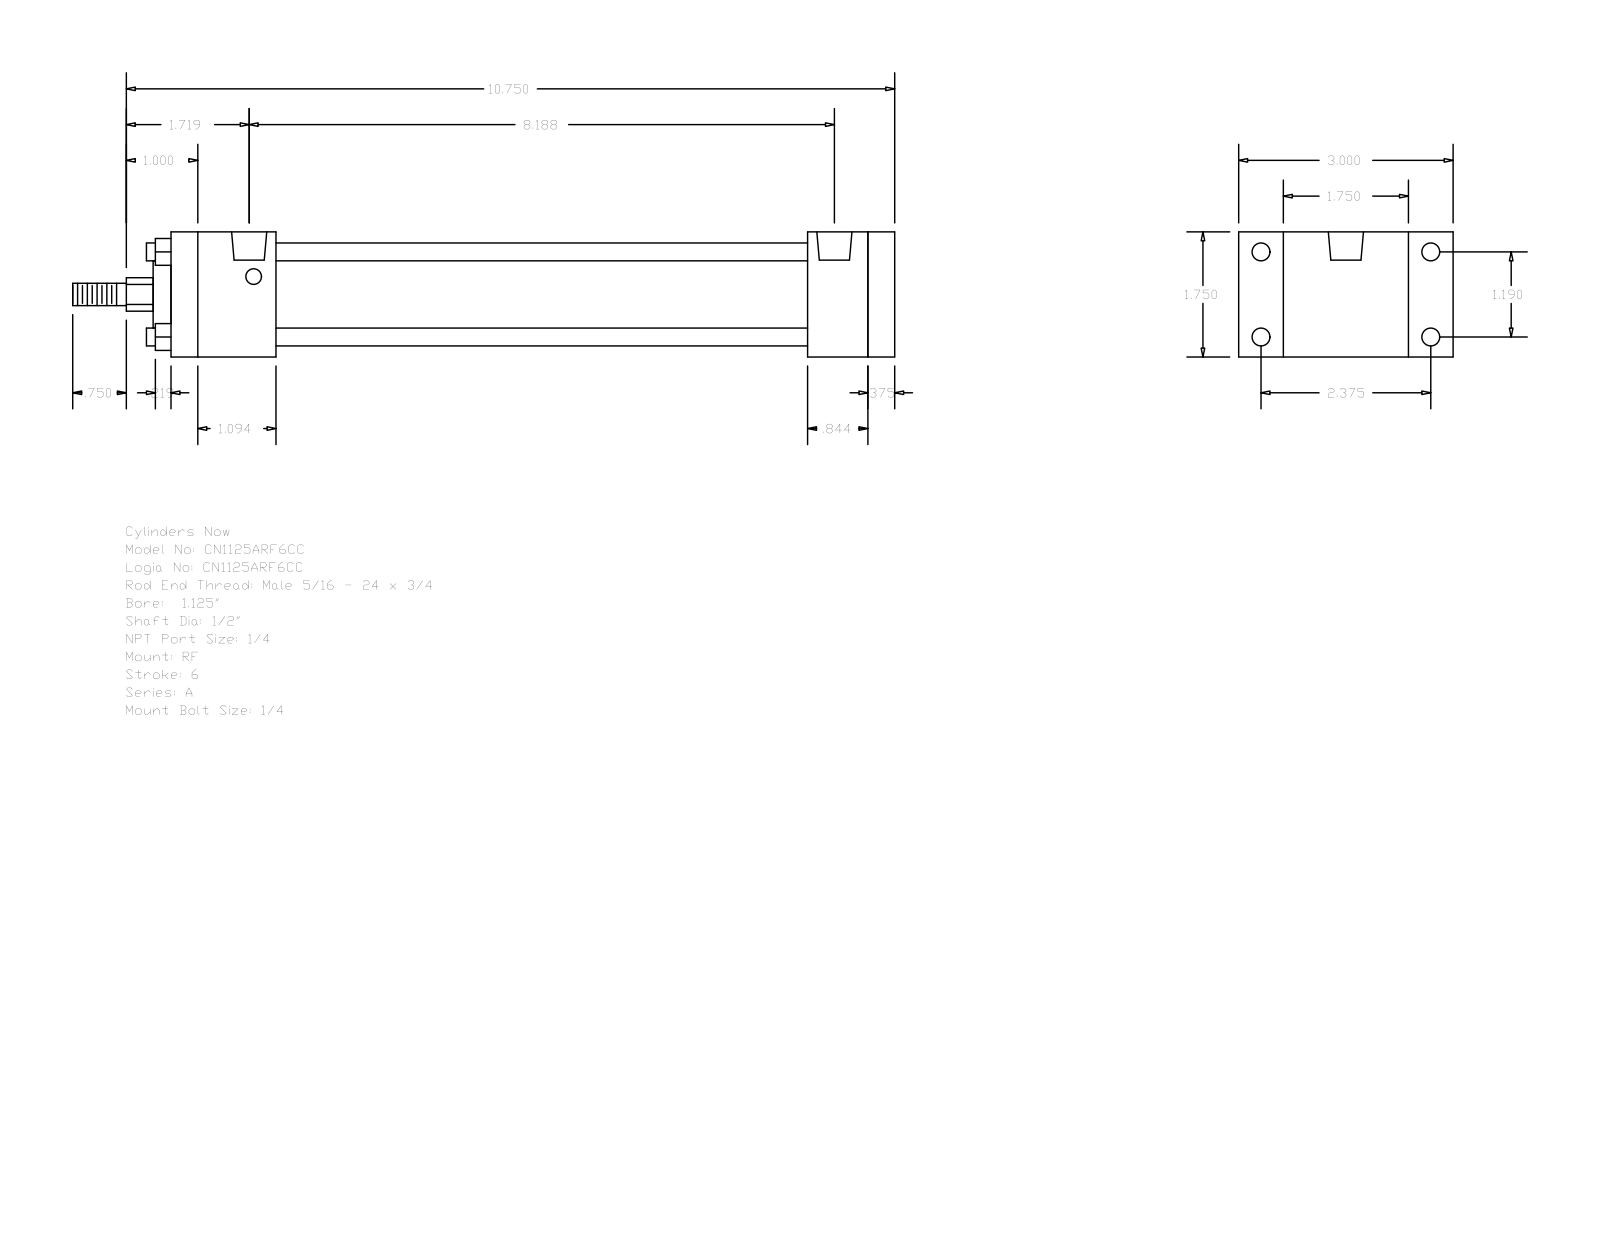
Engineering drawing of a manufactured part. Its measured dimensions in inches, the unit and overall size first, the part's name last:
Units: inches
Overall size (bounding box): 11.5 × 3 × 1.75
Round holes (diameter × count): ⌀0.219 ×4, ⌀0.25 ×4, ⌀0.492 ×2
Round bosses / shafts (diameter × count): ⌀0.25 ×4, ⌀1.255 ×1, ⌀0.937 ×1, ⌀0.5 ×1, ⌀0.313 ×1
Partial cylindrical surfaces — rounded edges, fillets, slot ends (radius × count): R0.234 ×1
Main face-to-face distances: 1.75, 0.375, 10.125, 9.75, 1.469, 8.906, 7.437, 8.281, 8.656, 0.844
Hole centre spacings: 1.19, 2.375, 2.656, 8.063, 0.062, 0.063, 8.125, 8.125
Bodies: 0 solids, 92 faces (64 planar, 28 cylindrical, 0 other)
Part name (STEP PRODUCT): A_RF__0112_0.5
STEP written by: GSSL Pune (CONFIG_CONTROL_DESIGN)
